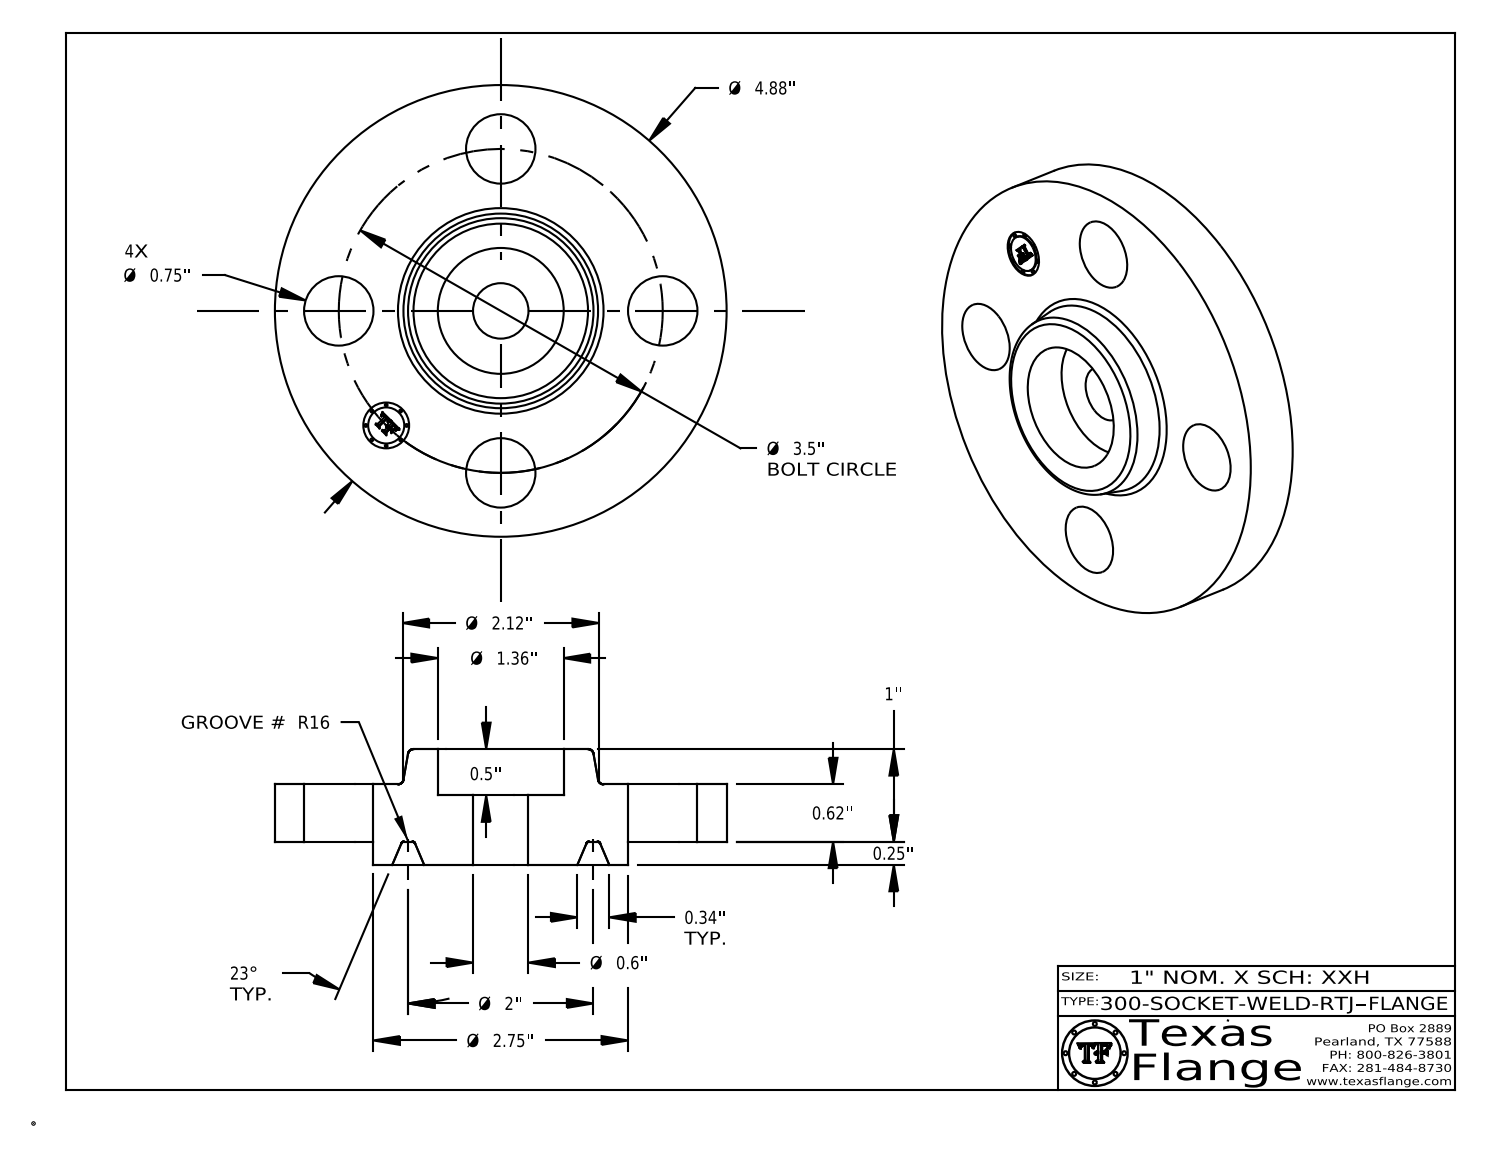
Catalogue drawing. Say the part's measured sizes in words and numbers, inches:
The part is named "300-SOCKET-WELD-RTJ". Its 3-D file was written by "CATIA V5 STEP AP214 (AUTOMOTIVE_DESIGN)". It is 1 solid with 422 faces: 372 planar, 36 cylindrical and 14 other. Overall it measures 4.88 by 4.88 by 1.25 inches. Its volume is 11.93 cubic inches and its surface area 58.32 square inches. Round holes: 4 of diameter 0.75, 1 of diameter 0.495, 1 of diameter 0.599, 1 of diameter 1.36. Round bosses or shafts: 8 of diameter 0.03, 1 of diameter 4.88, 1 of diameter 2.75, 1 of diameter 0.39. The main face-to-face distances are 0.62, 0.25, 0.87, 0.5, 1.25, 1, 0.38, 0.75, 0.12, 0.105. The hole center spacings are 1.75, 2.475, 1.339, 3.233, 3.5.
